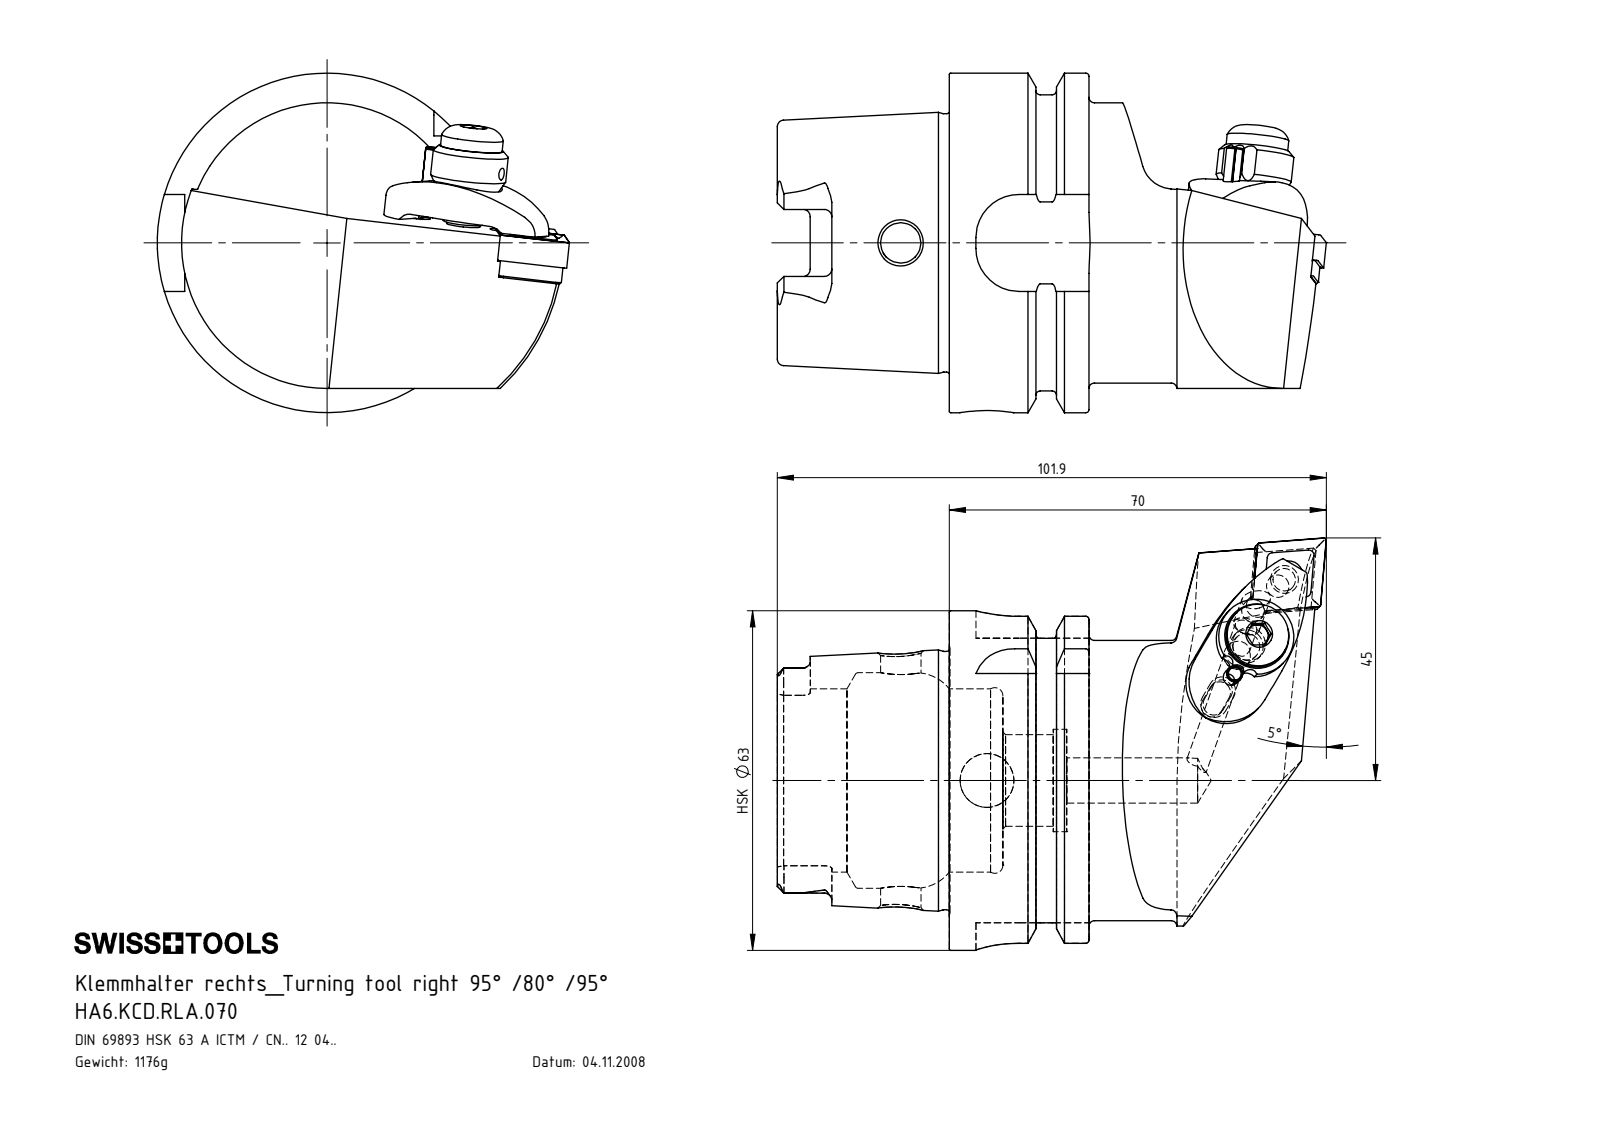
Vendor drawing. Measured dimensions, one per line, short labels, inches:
name: WCD-ER2.101.003_A; WCC-ER2.001.010_A; KVT_MB_600_050; CNMG120404 (+7 more)
written by: SolidWorks 2017 (AUTOMOTIVE_DESIGN)
unit: in
bodies: 11 solids, 470 faces (125 planar, 153 cylindrical, 192 other)
size: 4.012 × 3.012 × 2.48
volume: 9.091 in³; area: 55.01 in²
holes: 3× ⌀0.079, 3× ⌀0.165, 2× ⌀0.197, 2× ⌀0.276, 1× ⌀0.094, 1× ⌀0.118, 1× ⌀0.157, 1× ⌀0.203, 1× ⌀0.244, 1× ⌀0.258, 1× ⌀0.295, 1× ⌀0.331
bosses: 2× ⌀0.197, 2× ⌀0.118, 1× ⌀2.48, 1× ⌀2.163, 1× ⌀2.047, 1× ⌀1.887, 1× ⌀0.551, 1× ⌀0.453
rounds: 6× R0.015, 6× R0.027, 6× R0.055, 4× R0.016, 4× R0.039, 4× R0.113, 4× R0.315, 3× R0.059
face distances: 1.022, 0.63, 0.392, 1.256, 1.648, 2.278, 2.079, 0.858, 0.467, 2.114
hole spacings: 0.287, 0.315, 0.323, 0.595, 0.903, 0.906, 0.279, 0.315
